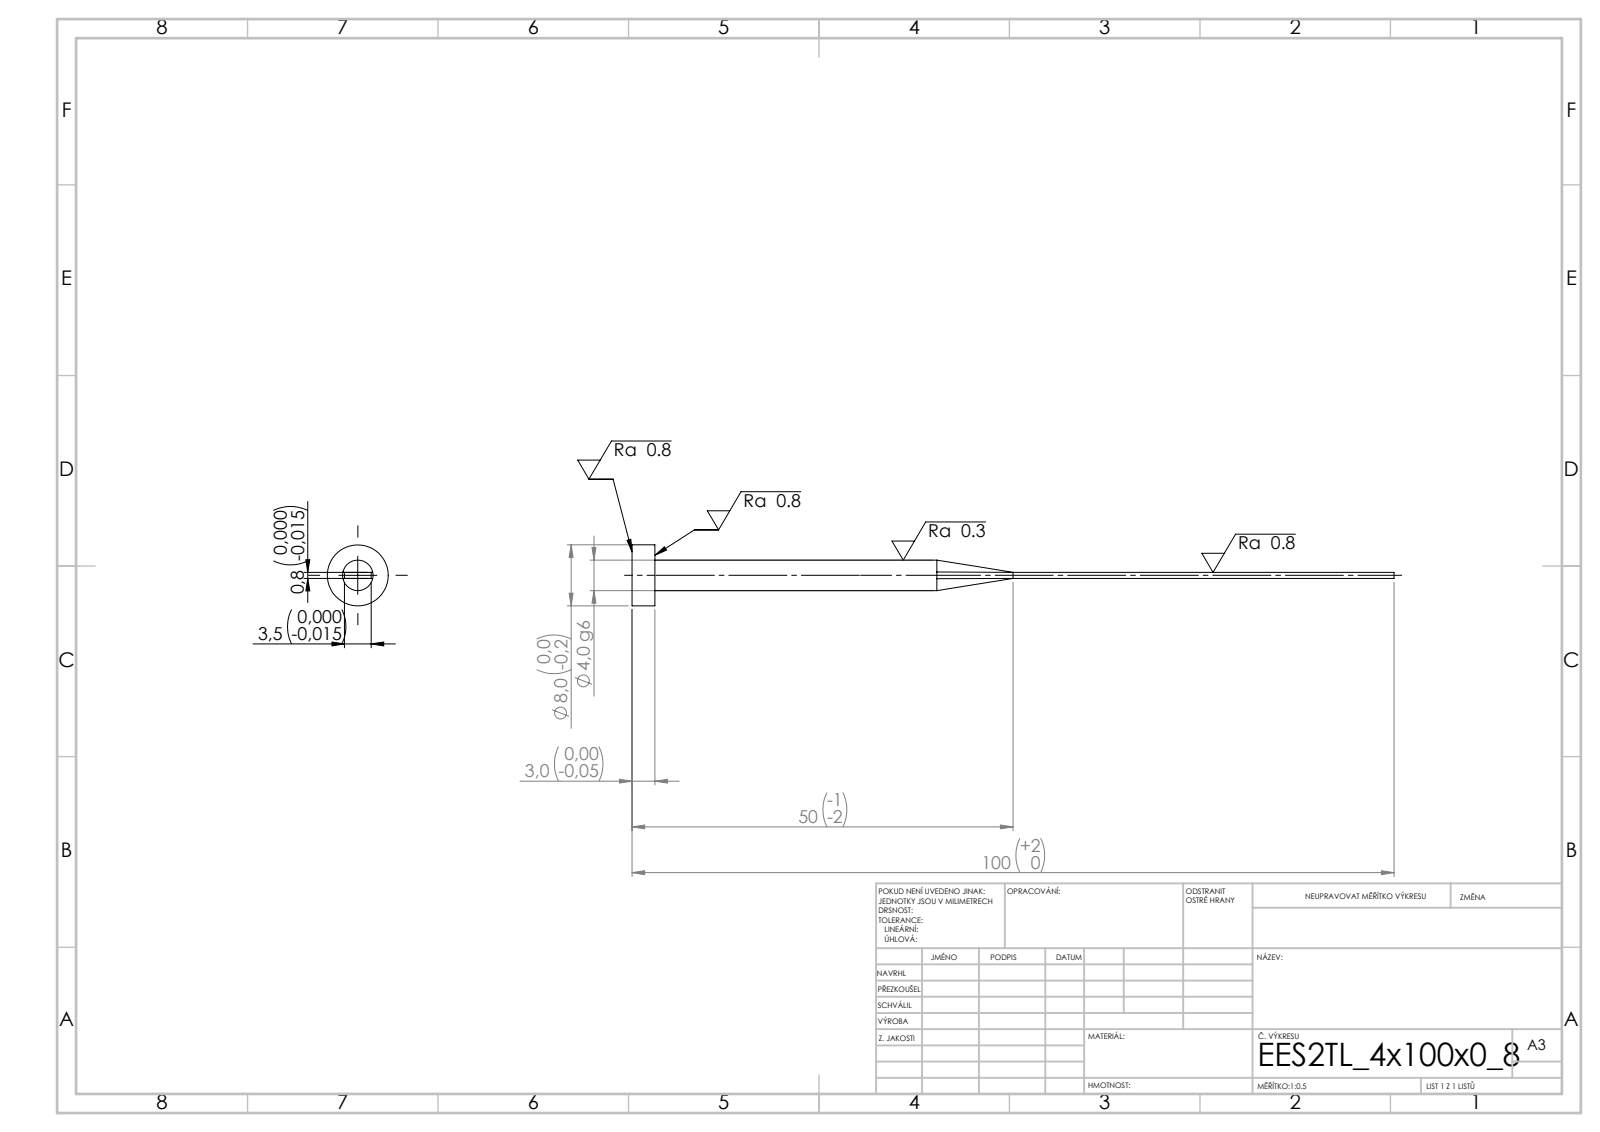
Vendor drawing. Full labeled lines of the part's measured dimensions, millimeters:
STEP written by: SolidWorks 2019 (CONFIG_CONTROL_DESIGN)
Units: millimetres
Bodies: 1 solid, 15 faces (7 planar, 4 cylindrical, 4 other)
Overall size (bounding box): 100 × 8 × 8
Volume: 828 mm³ · Surface area: 1 163 mm²
Round bosses / shafts (diameter × count): ⌀8 ×1, ⌀4 ×1
Main face-to-face distances: 0.8, 3.5, 3, 100, 97
